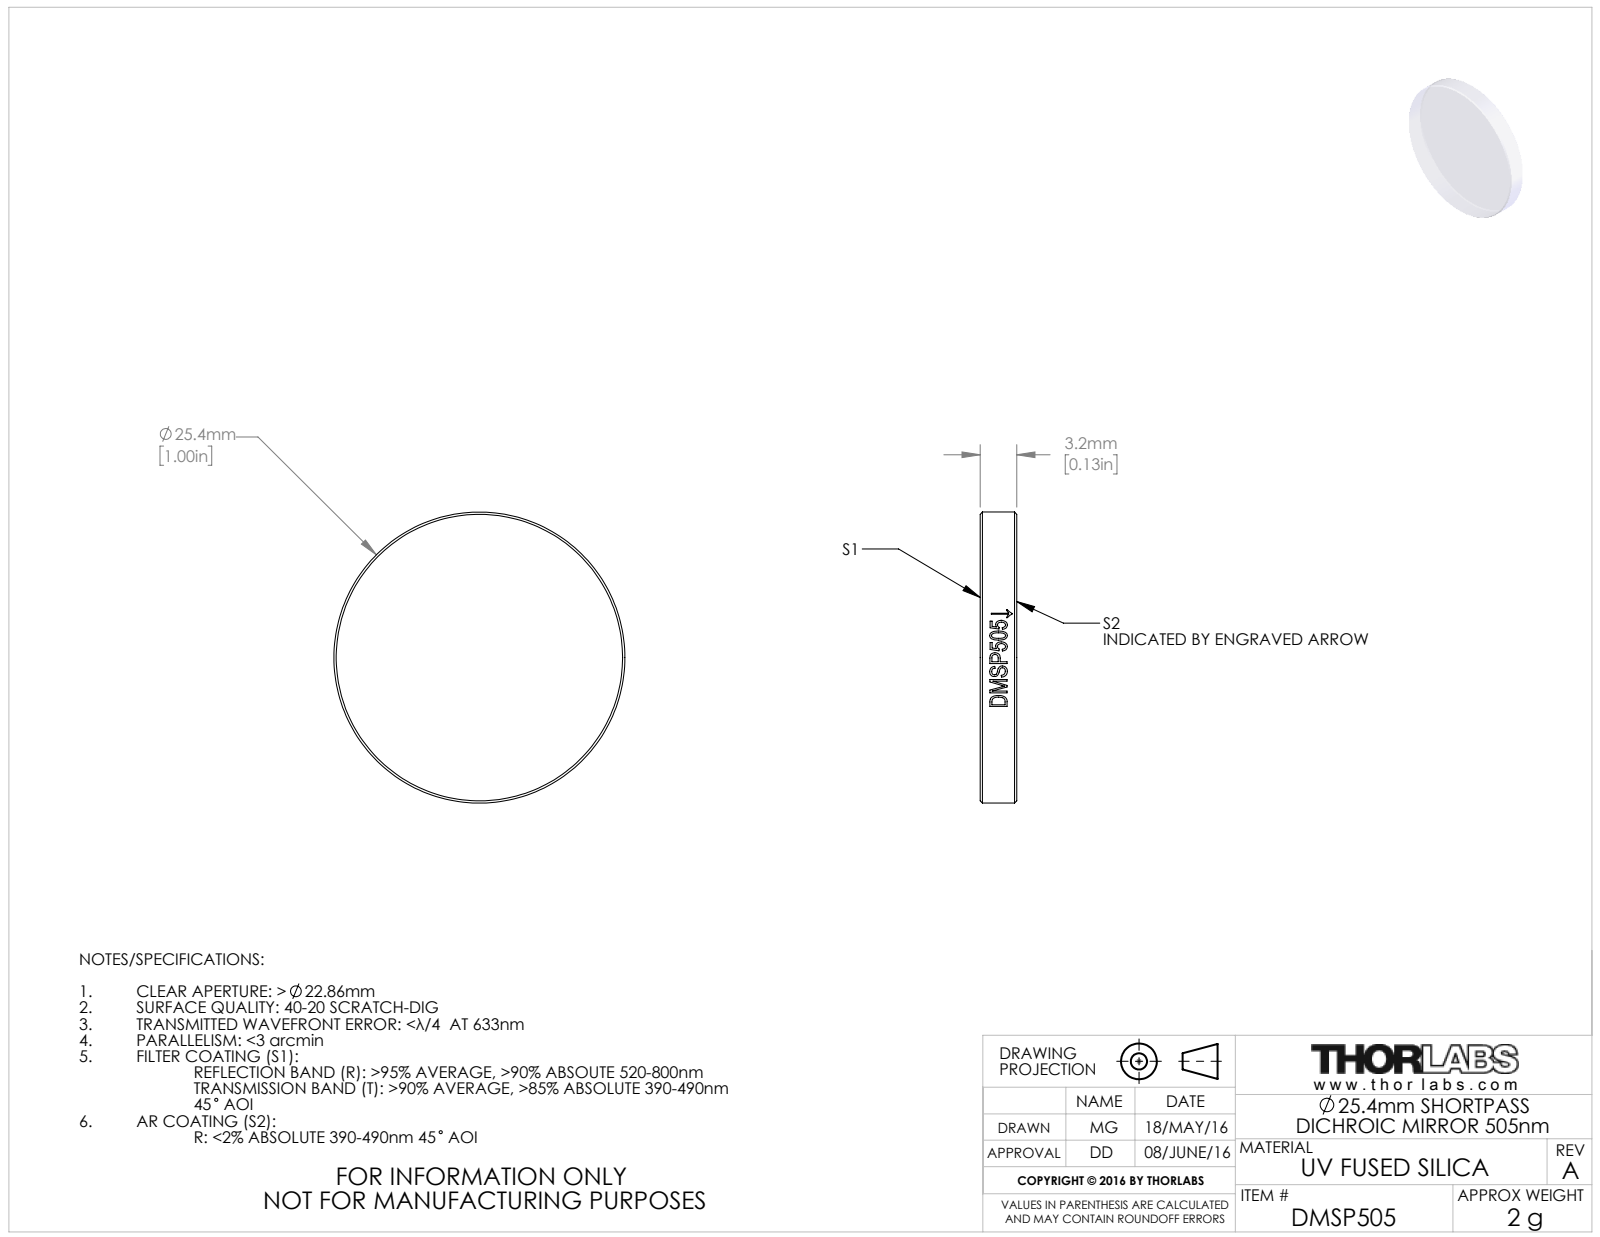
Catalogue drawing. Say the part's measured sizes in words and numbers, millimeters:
The part is named "TTN045148-E0W". Its 3-D file was written by "SolidWorks 2016 (CONFIG_CONTROL_DESIGN)". It is 1 solid with 19 faces: 2 planar, 13 cylindrical and 4 other. Overall it measures 25.4 by 25.4 by 3.2 millimeters. Its volume is 1 618 cubic millimeters and its surface area 1 250 square millimeters. Round bosses or shafts: 1 of diameter 25.4. The main face-to-face distances are 3.2.
